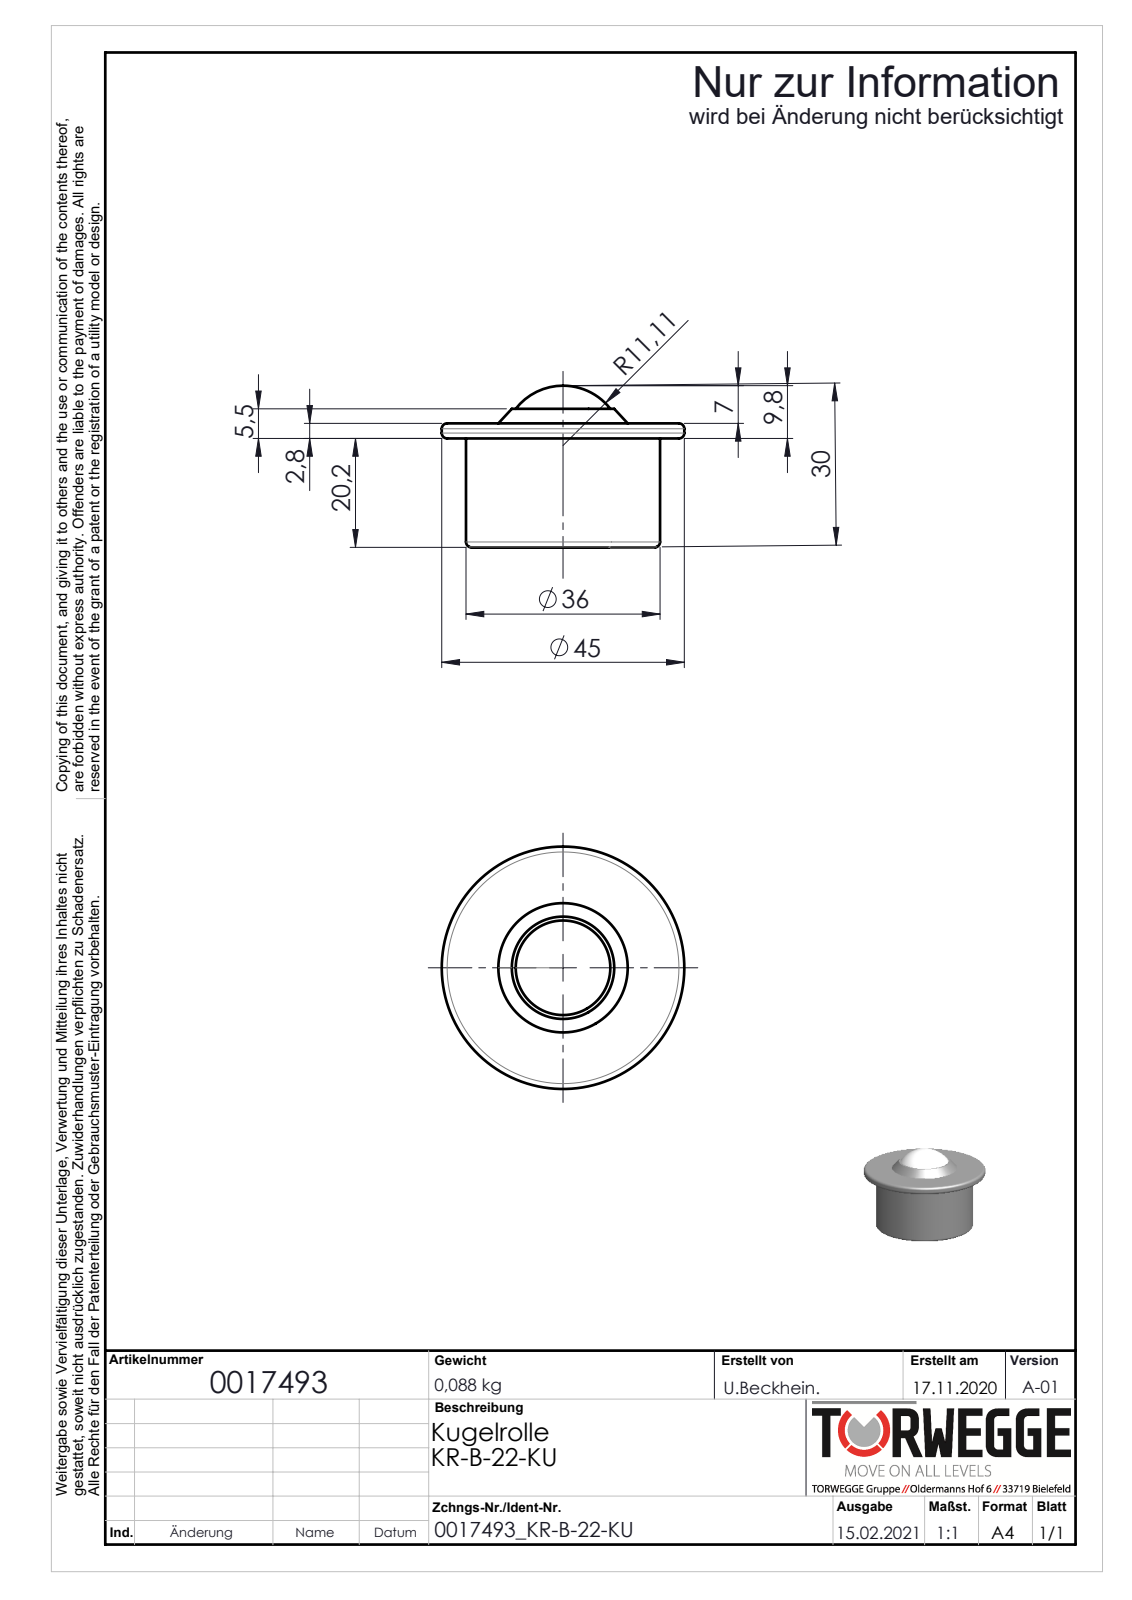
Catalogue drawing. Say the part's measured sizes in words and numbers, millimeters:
The part is named "0017493". Its 3-D file was written by "SolidWorks 2020 (AUTOMOTIVE_DESIGN)". It is 1 solid with 39 faces: 5 planar, 8 cylindrical and 26 other. Overall it measures 45 by 45 by 30.02 millimeters. Its volume is 25 180 cubic millimeters and its surface area 5 978 square millimeters. Round holes: 1 of diameter 2.5, 1 of diameter 7. Round bosses or shafts: 1 of diameter 45, 1 of diameter 36. The main face-to-face distances are 2.8, 5.5, 2.7, 18.2, 21, 23.7, 1.25, 16.95, 19.75, 22.45.
